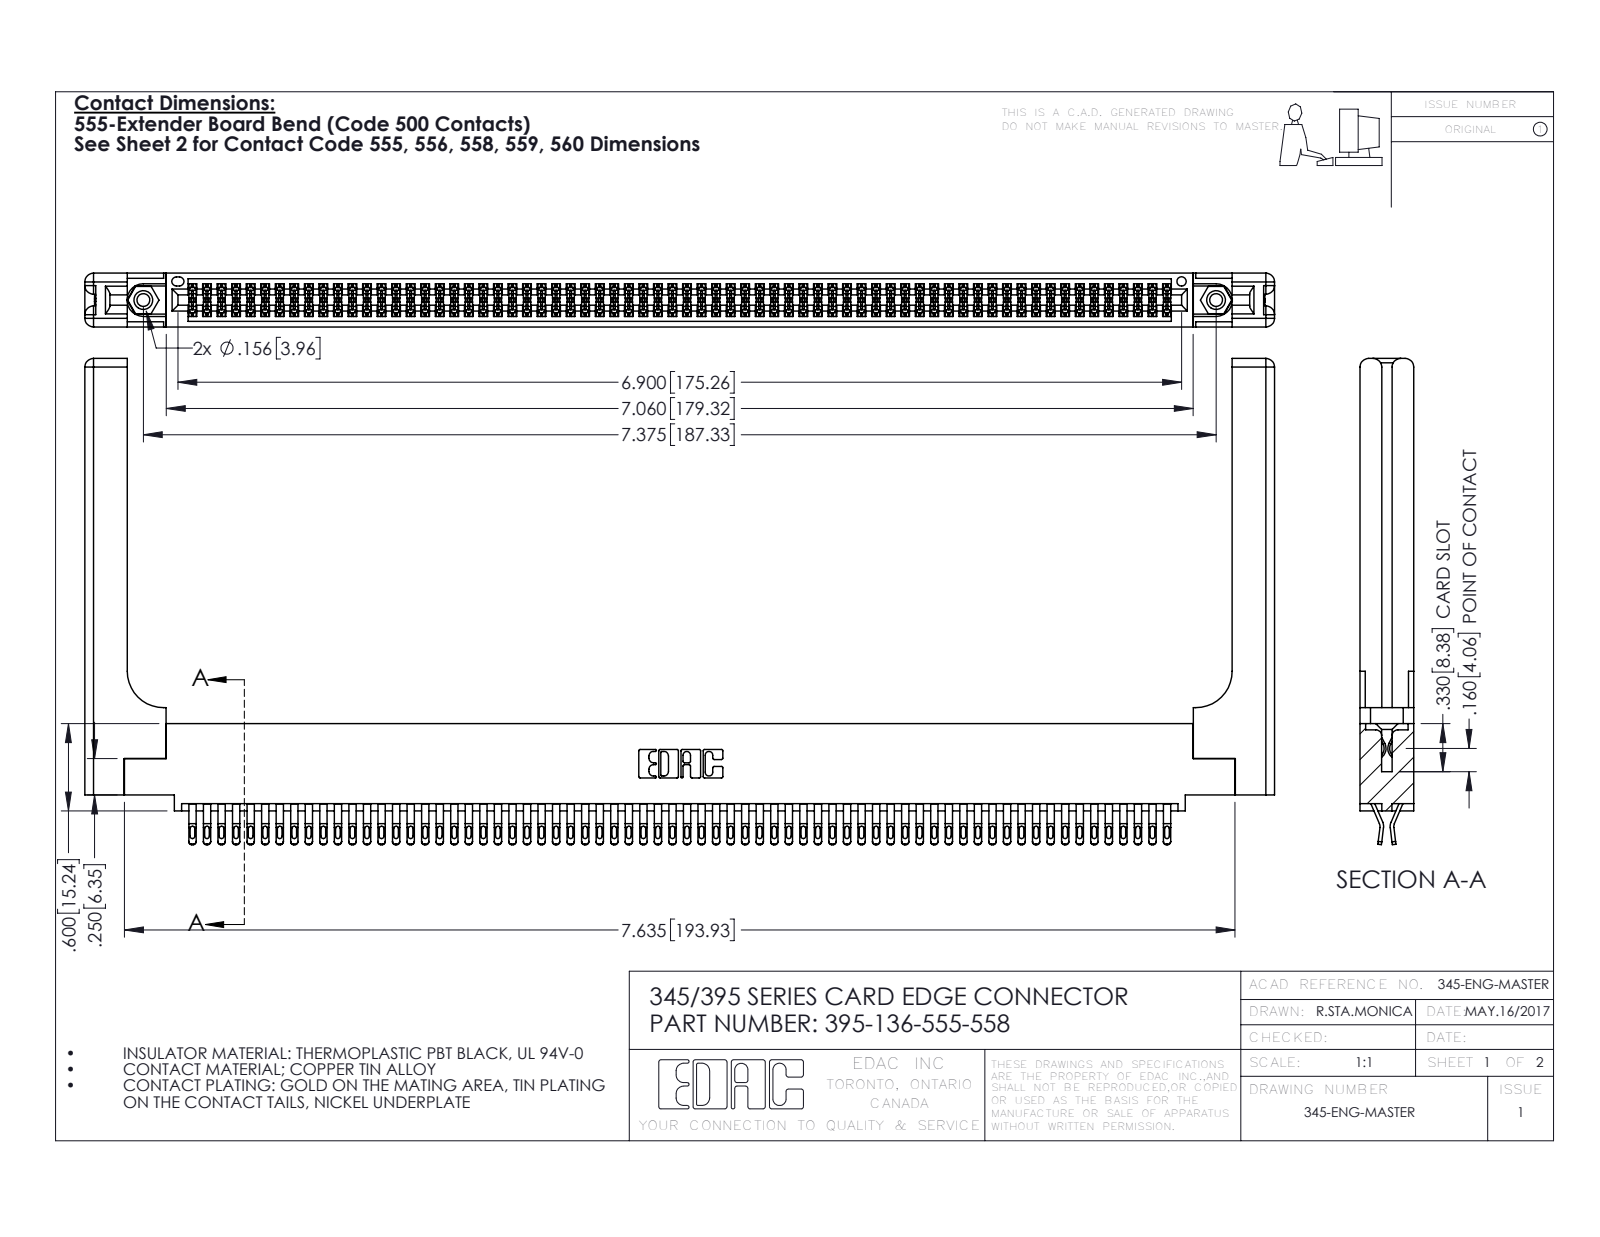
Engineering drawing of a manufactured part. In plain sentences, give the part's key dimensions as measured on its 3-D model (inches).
The part is named "345-250-001_345-250-001-102; 395-136-555-558; 345-220-058_345-220-058; 345-292-001_555 Tail (+1 more)". Its 3-D file was written by "SolidWorks 2016 (CONFIG_CONTROL_DESIGN)". It is 141 solids with 8002 faces: 4448 planar, 3494 cylindrical and 60 other. Overall it measures 8.179 by 3.342 by 0.37 inches. Its volume is 1.783 cubic inches and its surface area 58.42 square inches. Round holes: 2 of diameter 0.089, 2 of diameter 0.125, 2 of diameter 0.156, 1 of diameter 0.064. Round bosses or shafts: 2 of diameter 0.155. Partial cylindrical surfaces (rounded edges, fillets, slot ends): 340 of radius 0.016, 272 of radius 0.02, 204 of radius 0.006, 22 of radius 0.01, 16 of radius 0.06, 6 of radius 0.007, 6 of radius 0.031, 3 of radius 0.026. The main face-to-face distances are 0.072, 0.298, 0.37, 0.025, 0.098, 0.272, 0.2, 0.225, 0.148, 0.15. The hole center spacings are 0.27, 7.139, 7.375.
